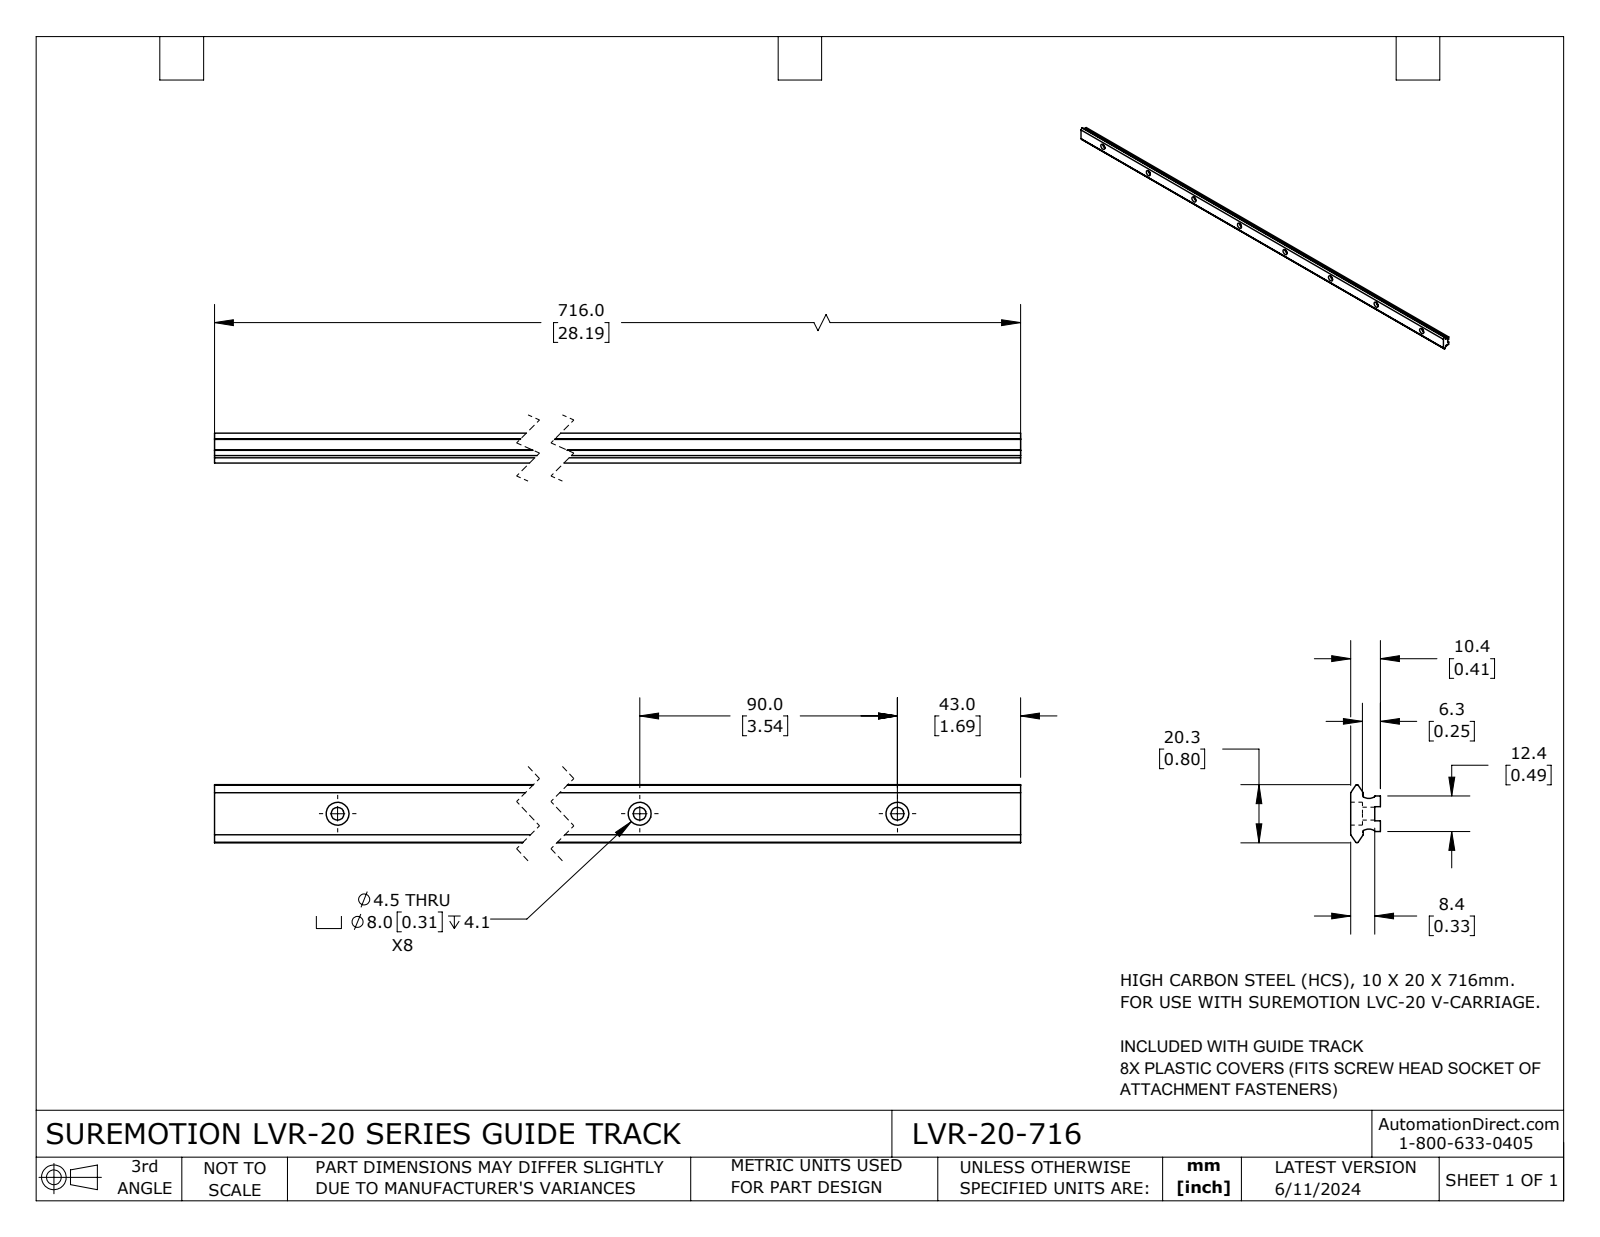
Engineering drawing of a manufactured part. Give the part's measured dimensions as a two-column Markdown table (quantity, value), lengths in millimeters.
| quantity | value |
| --- | --- |
| part name | LVR-20-716 |
| STEP written by | SolidWorks 2023 (CONFIG_CONTROL_DESIGN) |
| units | millimeters |
| bodies | 1 solid, 66 faces (24 planar, 42 cylindrical, 0 other) |
| overall size | 716 × 20.27 × 10.41 |
| volume | 96 232 mm³ |
| surface area | 45 365 mm² |
| round holes (diameter × count) | 4.5 × 8, 8 × 8 |
| partial cylindrical surfaces (radius × count) | 0.4 × 4, 0.5 × 2, 3.84 × 2 |
| main face-to-face distances | 10.41, 2, 8.41, 3.7, 8.7, 12.06, 12.05, 5, 12.4, 5.99 |
| hole center spacings | 90, 180, 270, 360, 450, 540, 630 |
